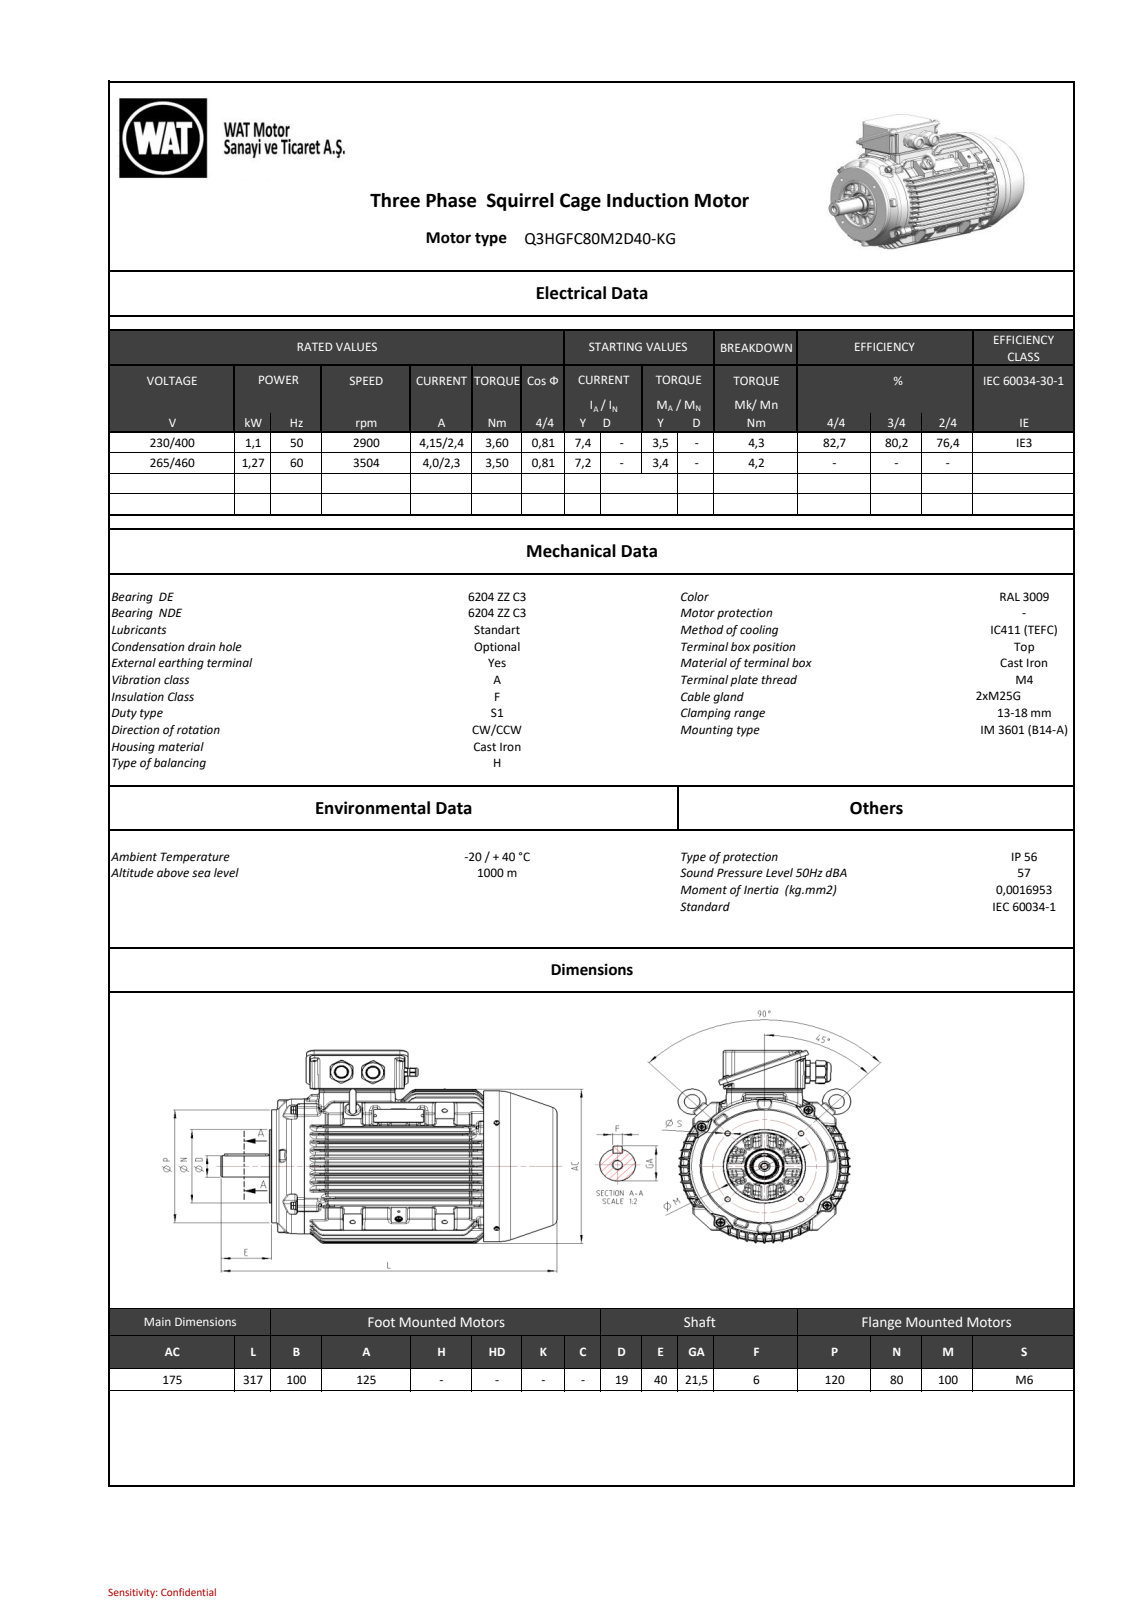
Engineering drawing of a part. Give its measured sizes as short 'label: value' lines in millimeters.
name: 260051B46F5629o7
written by: SIEMENS PLM Software NX 11.0 (AUTOMOTIVE_DESIGN)
unit: mm
bodies: 0 solids, 2813 faces (782 planar, 807 cylindrical, 1224 other)
size: 316.76 × 232.47 × 221.33
holes: 5× ⌀5, 3× ⌀10, 2× ⌀2.5, 2× ⌀17.2, 1× ⌀6.4, 1× ⌀6.5, 1× ⌀27.8, 1× ⌀28, 1× ⌀168
bosses: 4× ⌀20, 3× ⌀9.2, 3× ⌀8.65, 3× ⌀8.5, 3× ⌀8, 3× ⌀5, 2× ⌀27.7, 2× ⌀25.25
rounds: 322× R1.5, 57× R2.5, 38× R1.8, 30× R1, 24× R2, 20× R0.2, 18× R4, 13× R3
face distances: 41.78, 62.56, 276.76, 234.98, 3.01, 3, 1.5, 1.53, 2.98, 59.58
hole spacings: 70.71, 50, 100, 40, 49.99, 50.01, 74.99, 77.95
